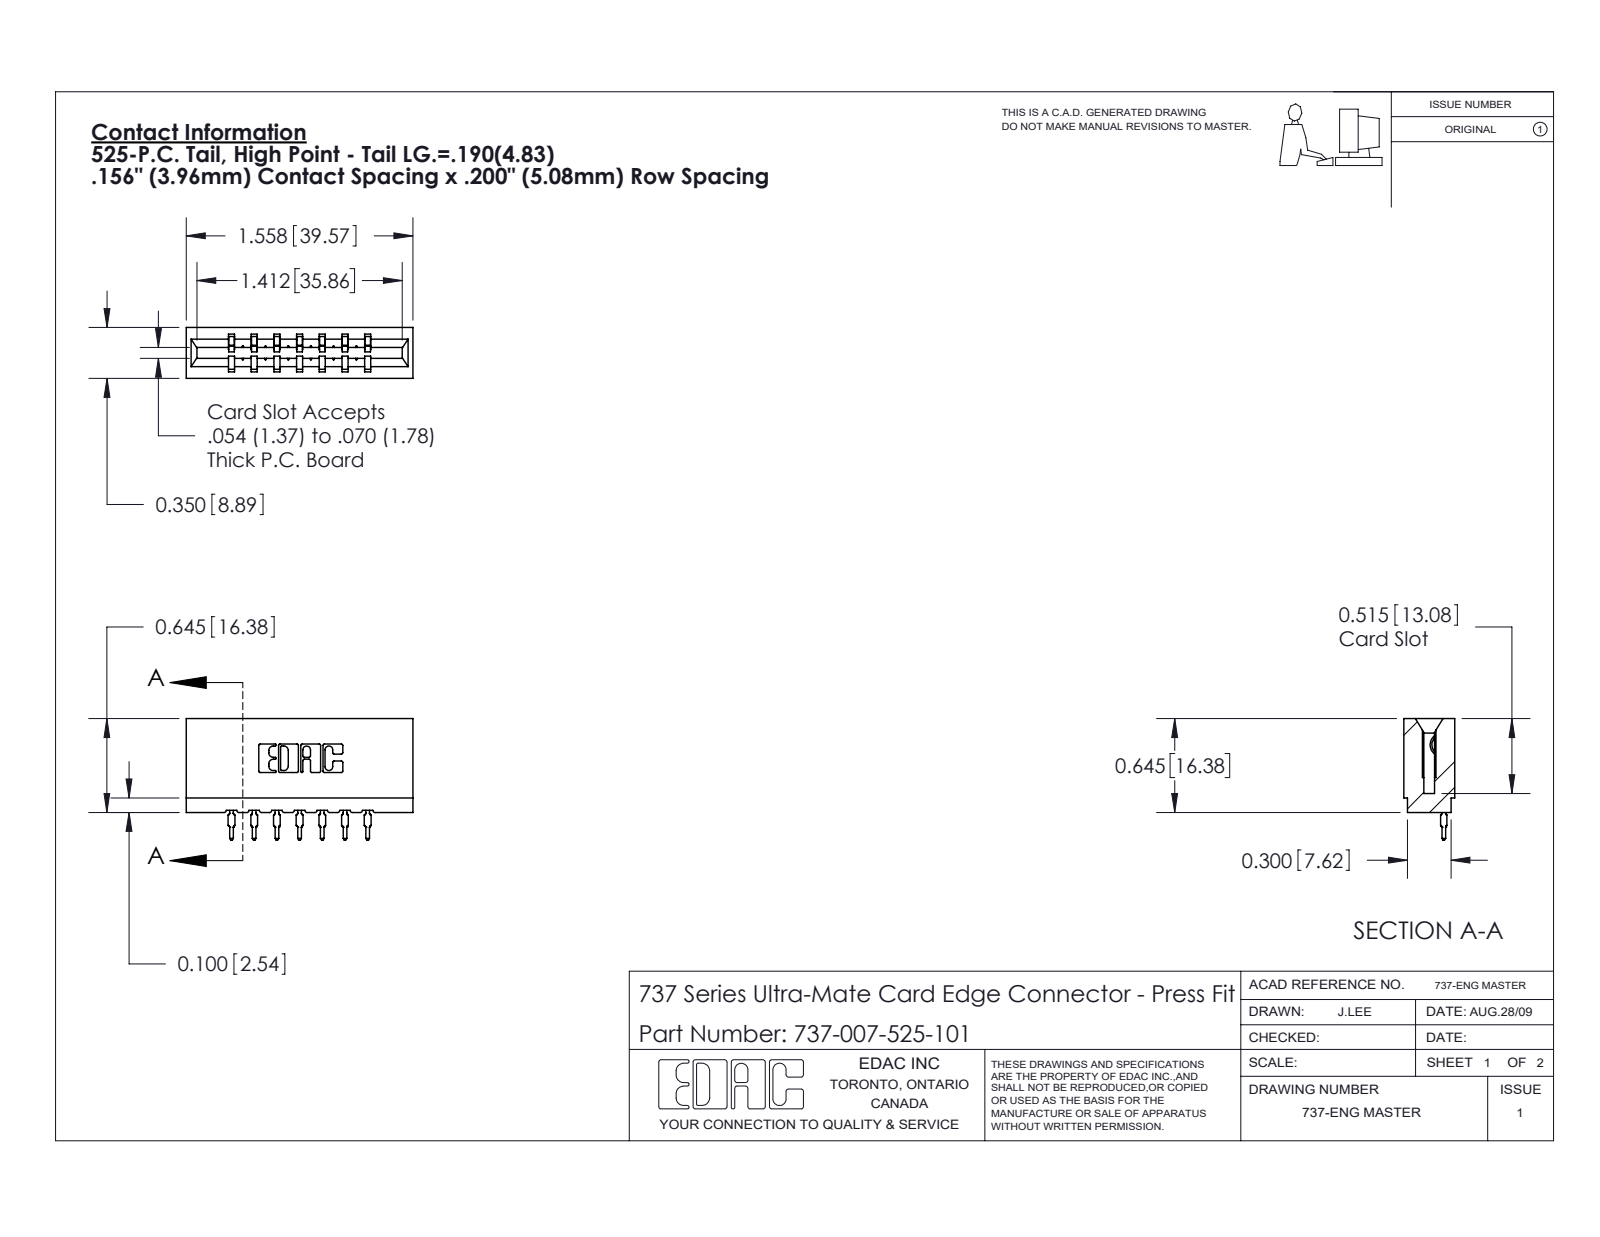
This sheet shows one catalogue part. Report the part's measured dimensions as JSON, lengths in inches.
{"part_name": "745-292-001_525; 737 Part_Insulator Option - 01; 737-007-525-101", "step_written_by": "SolidWorks 2020 (CONFIG_CONTROL_DESIGN)", "units": "inches", "bodies": {"solids": 8, "faces": 885, "planar": 530, "cylindrical": 173, "other": 182}, "overall_size": [1.558, 0.836, 0.35], "volume_in3": 0.248, "surface_area_in2": 7.427, "partial_cylinders_radius": [[0.01, 22], [0.015, 14], [0.021, 14], [0.007, 6], [0.031, 6], [0.005, 4], [0.011, 4], [0.026, 3]], "face_to_face_distances": [0.156, 0.138, 0.212, 0.35, 0.312, 0.354, 0.198, 0.624, 0.468, 0.074]}
